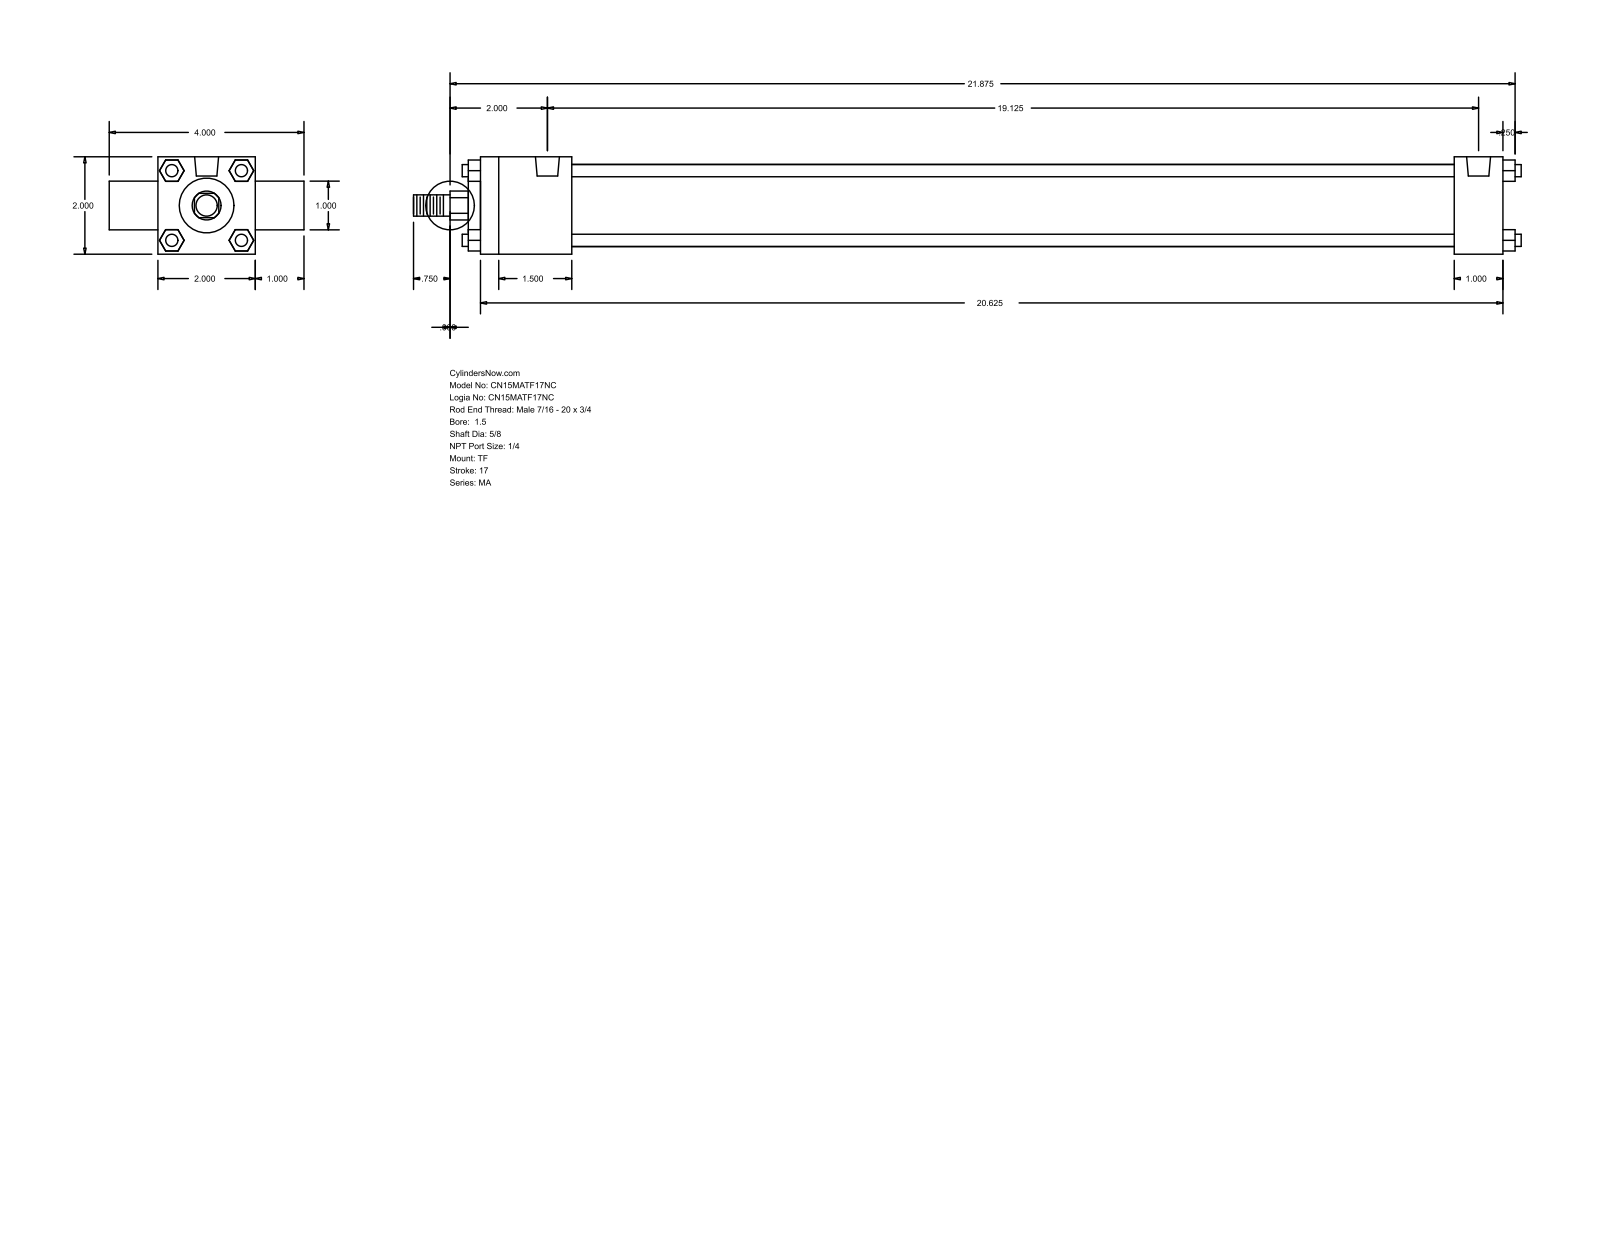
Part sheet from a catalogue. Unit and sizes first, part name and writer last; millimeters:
Units: millimetres
Overall size (bounding box): 577.85 × 101.6 × 50.8
Round holes (diameter × count): ⌀7.94 ×3, ⌀12.49 ×2
Round bosses / shafts (diameter × count): ⌀6.35 ×4, ⌀42.93 ×1, ⌀28.57 ×1, ⌀25.4 ×1, ⌀15.88 ×1, ⌀11.11 ×1
Partial cylindrical surfaces — rounded edges, fillets, slot ends (radius × count): R7.54 ×1
Main face-to-face distances: 50.8, 533.39, 25.4, 6.35, 539.74, 76.2, 47.62, 508, 460.38, 485.77
Hole centre spacings: 485.78
Bodies: 0 solids, 120 faces (92 planar, 28 cylindrical, 0 other)
Part name (STEP PRODUCT): MA_TF__0150_0.625
STEP written by: GSSL Pune (CONFIG_CONTROL_DESIGN)
